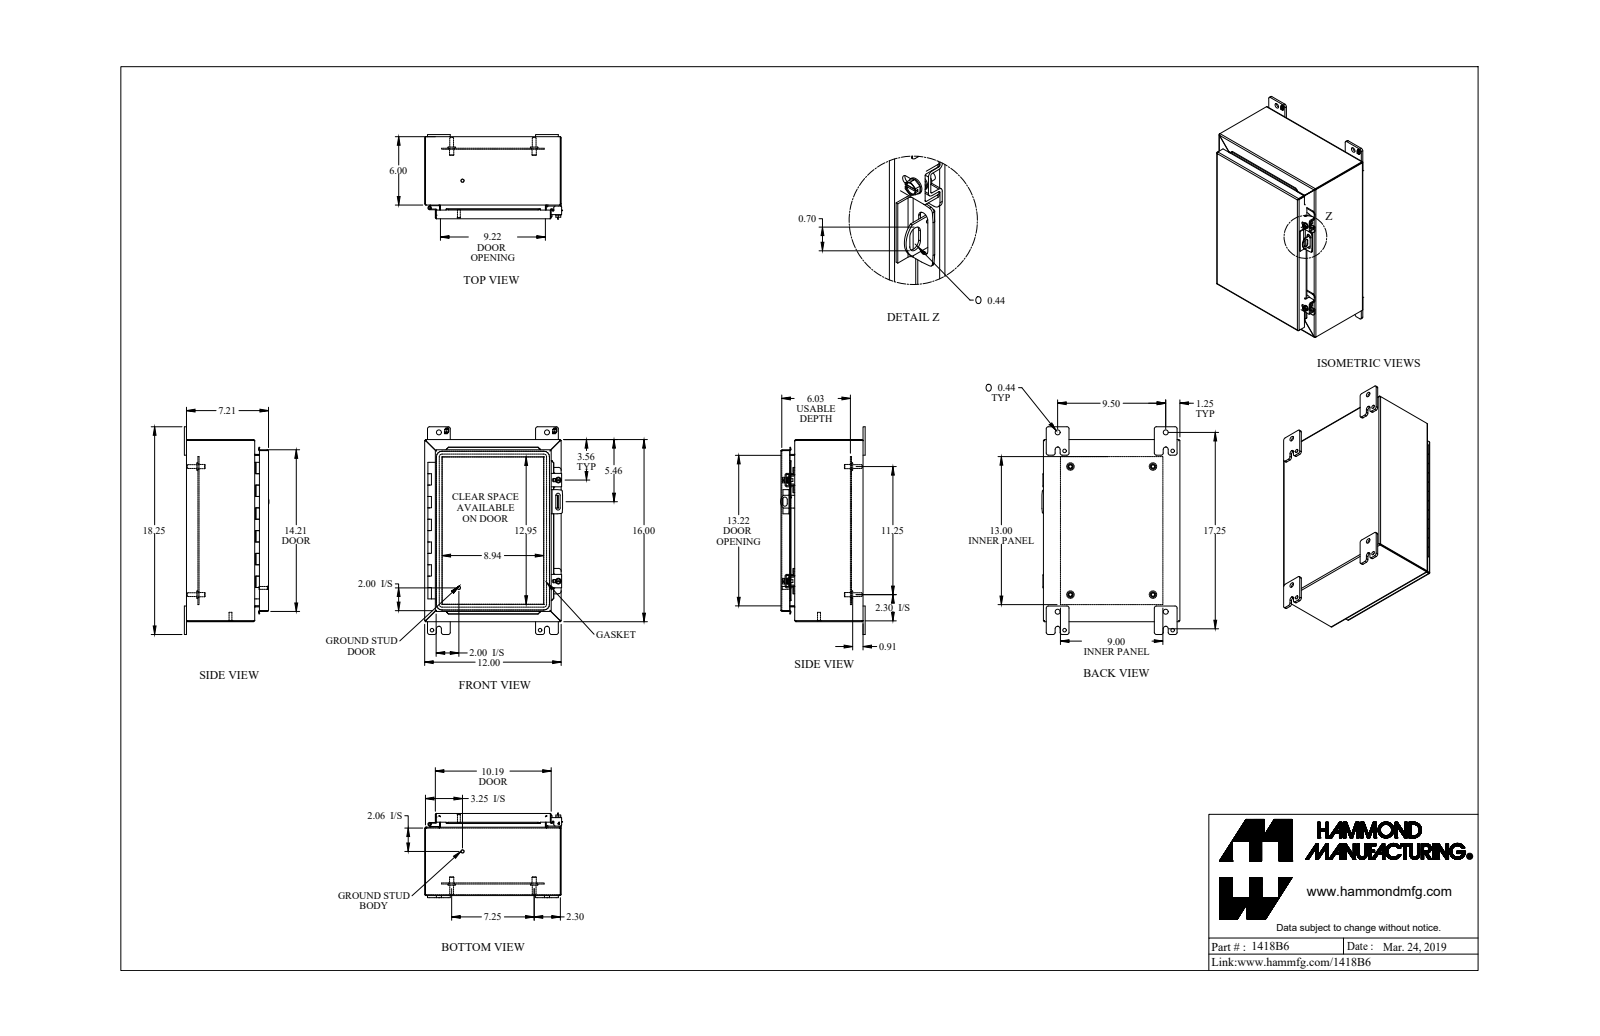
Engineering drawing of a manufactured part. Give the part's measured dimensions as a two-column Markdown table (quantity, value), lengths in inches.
| quantity | value |
| --- | --- |
| part name | 1418B6 |
| STEP written by | SolidWorks 2019 (AUTOMOTIVE_DESIGN) |
| units | inches |
| bodies | 38 solids, 955 faces (658 planar, 243 cylindrical, 54 other) |
| overall size | 18.25 × 12.125 × 7.437 |
| volume | 84.58 in³ |
| surface area | 2 188 in² |
| round holes (diameter × count) | 0.313 × 4, 0.437 × 4, 0.5 × 4, 0.213 × 2, 0.265 × 2, 0.307 × 2, 0.375 × 2, 0.445 × 2, 0.125 × 1, 0.187 × 1 |
| round bosses / shafts (diameter × count) | 0.65 × 4, 0.375 × 4, 0.33 × 4, 1 × 2, 0.5 × 2, 0.39 × 2, 0.281 × 2, 0.25 × 2 |
| partial cylindrical surfaces (radius × count) | 0.188 × 26, 0.036 × 20, 0.108 × 20, 0.048 × 13, 0.143 × 13, 0.007 × 8, 0.045 × 8, 0.079 × 8 |
| main face-to-face distances | 0.072, 7.113, 7.041, 11.928, 0.937, 7.185, 15.928, 1.009, 1.185, 5.928 |
| hole center spacings | 9.5, 18.393, 7.25, 8.508, 10.285, 12.8, 13.384, 1.735 |
